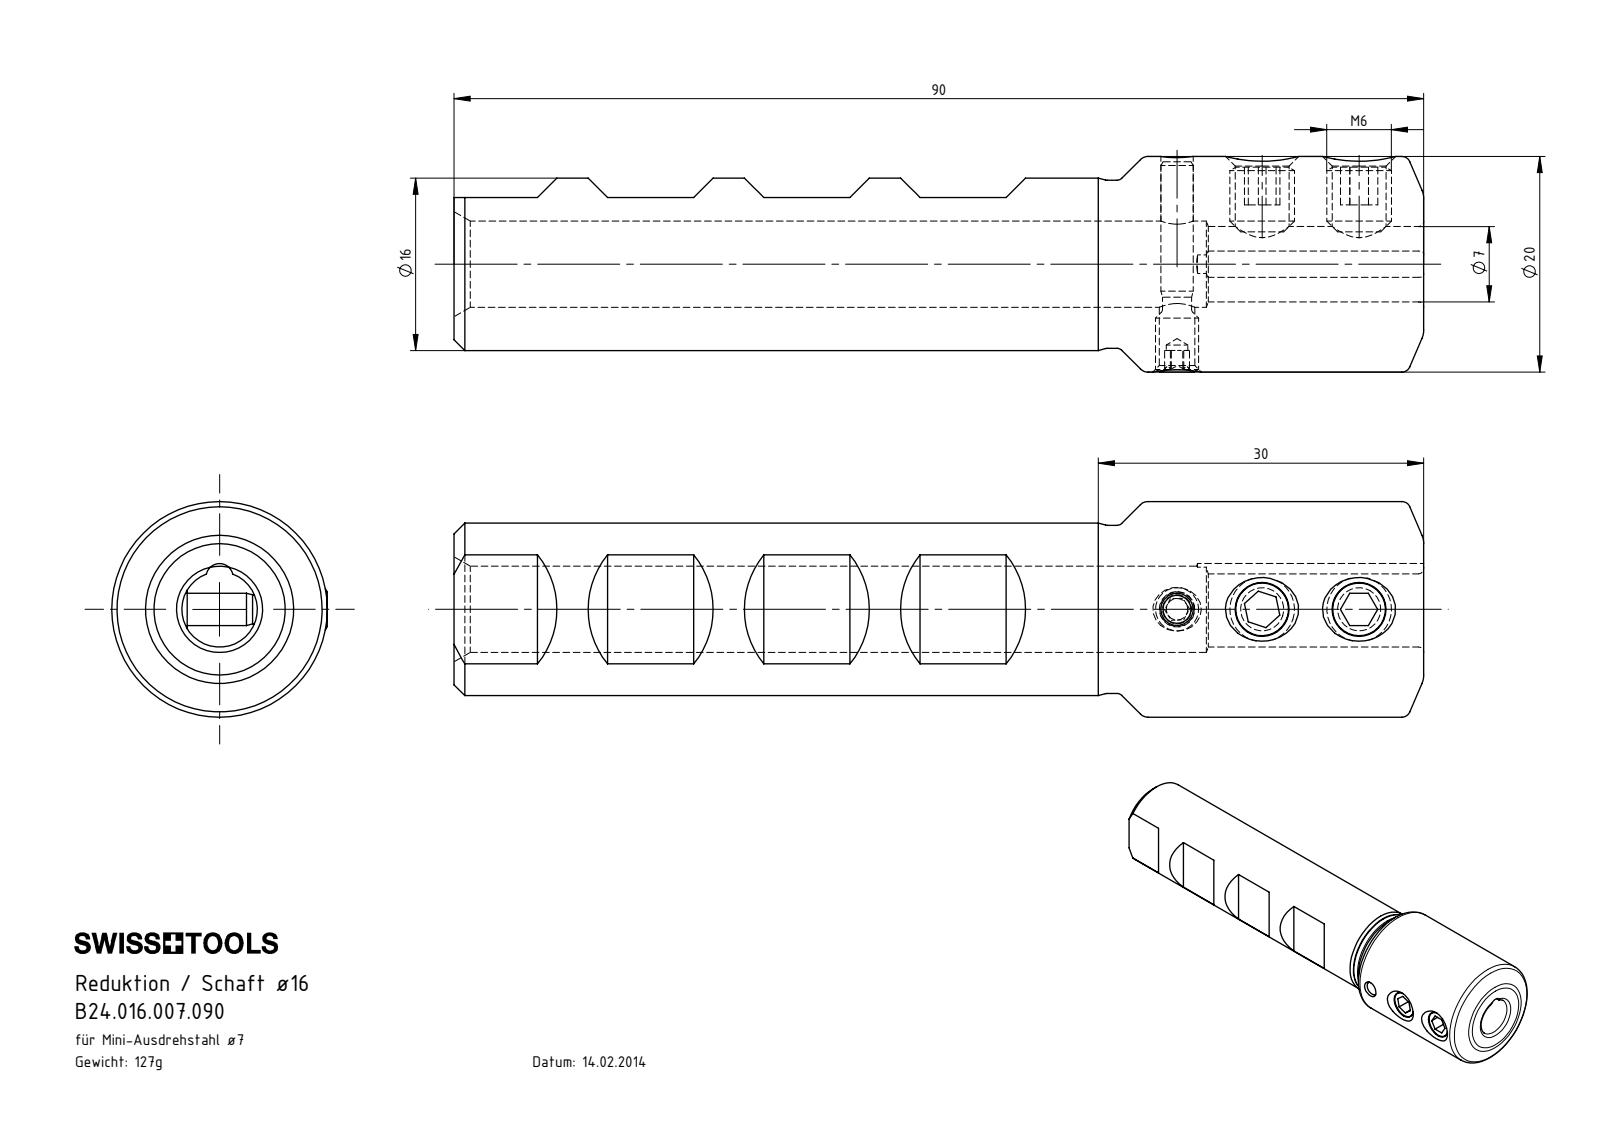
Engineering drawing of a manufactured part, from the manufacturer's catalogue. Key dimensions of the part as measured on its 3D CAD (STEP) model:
Part name (STEP PRODUCT): U0X-U16.0XX.090_A_Adapter 7; Axx-BG4.003.xxx_A_Adapter 7; ISO 4026 - M6 x 6; B24.016.007.090
STEP written by: SolidWorks 2017 (CONFIG_CONTROL_DESIGN)
Units: millimetres
Bodies: 4 solids, 130 faces (45 planar, 31 cylindrical, 54 other)
Overall size (bounding box): 90 × 20 × 20
Volume: 16 219 mm³ · Surface area: 8 239 mm²
Round holes (diameter × count): ⌀5 ×2, ⌀2 ×1, ⌀3 ×1, ⌀3.3 ×1, ⌀7 ×1, ⌀8 ×1
Round bosses / shafts (diameter × count): ⌀6 ×2, ⌀20 ×1, ⌀16 ×1, ⌀15.6 ×1, ⌀4 ×1, ⌀2.7 ×1
Partial cylindrical surfaces — rounded edges, fillets, slot ends (radius × count): R1.25 ×1
Main face-to-face distances: 10.25, 90, 20.5, 3, 6, 30.75, 2.5, 3.5, 3.22, 3.2
Hole centre spacings: 7.9, 9, 16.9
